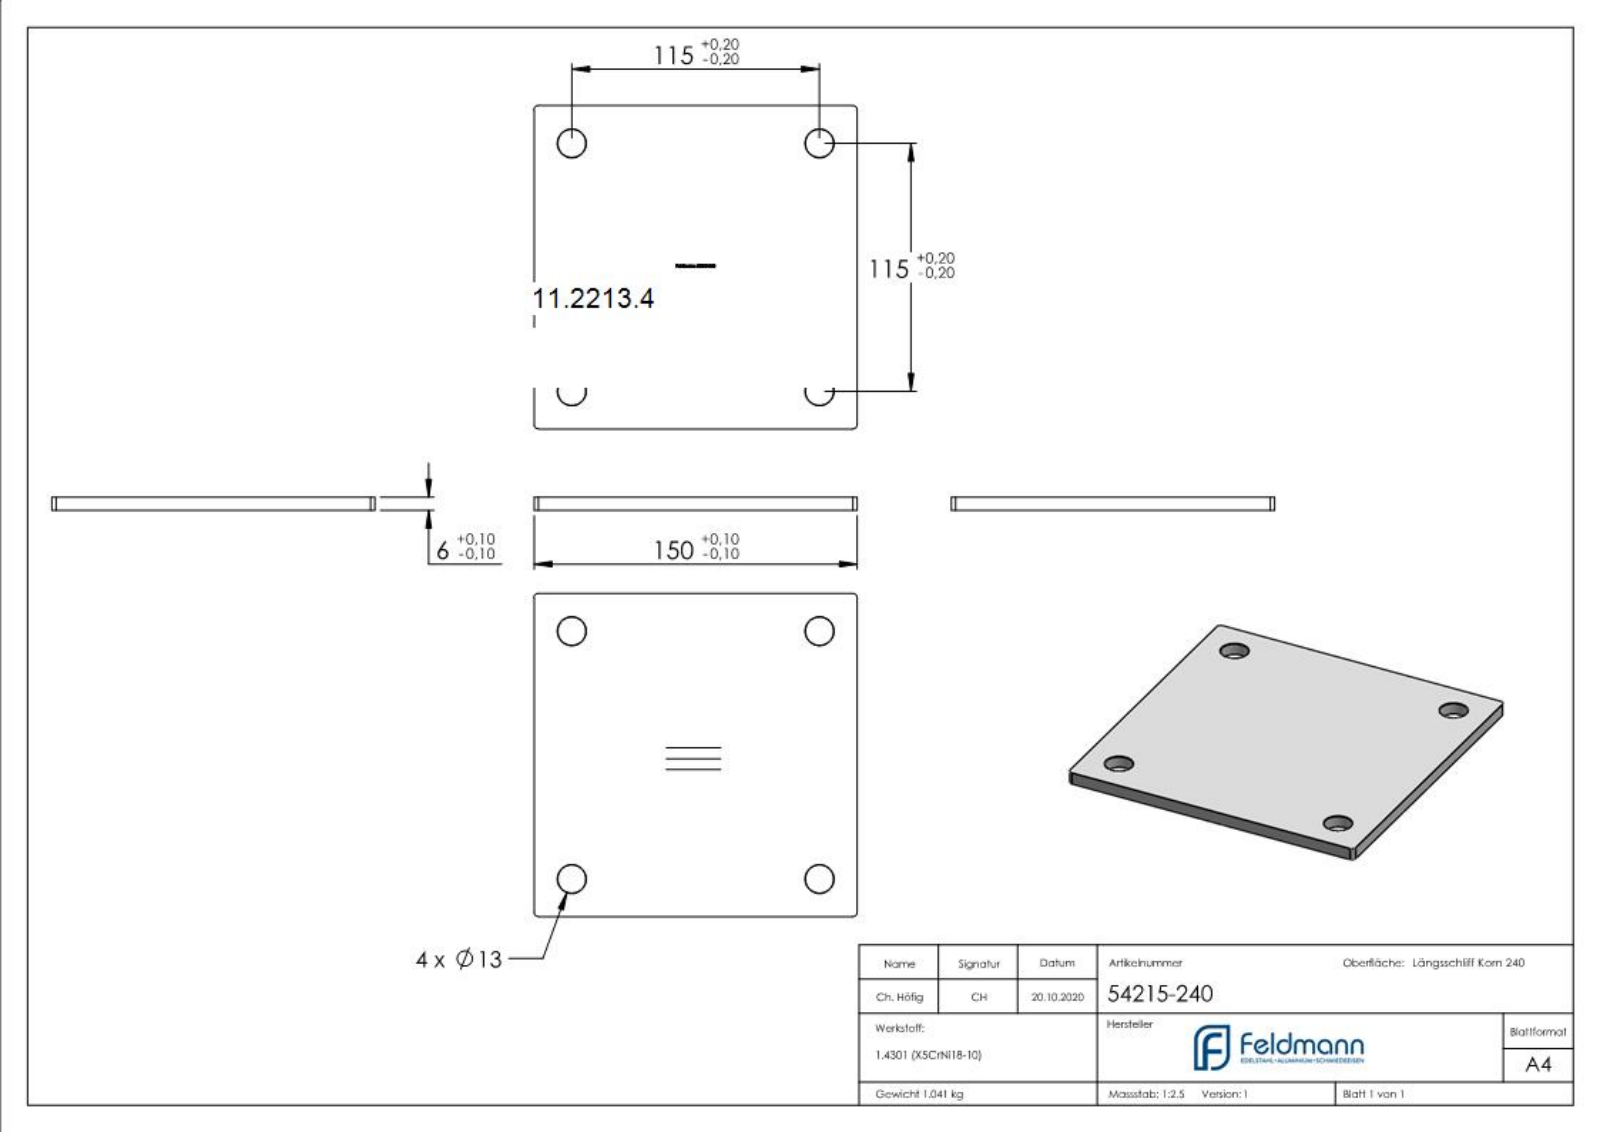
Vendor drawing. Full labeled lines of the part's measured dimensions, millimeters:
Part name (STEP PRODUCT): 54215-240
STEP written by: SolidWorks 2018 (CONFIG_CONTROL_DESIGN)
Units: millimetres
Bodies: 1 solid, 256 faces (143 planar, 12 cylindrical, 101 other)
Overall size (bounding box): 150 × 150 × 6
Volume: 131 783 mm³ · Surface area: 48 453 mm²
Round holes (diameter × count): ⌀13 ×4
Partial cylindrical surfaces — rounded edges, fillets, slot ends (radius × count): R2 ×4
Main face-to-face distances: 6, 150, 5.9, 75, 0.44, 0.88, 1.32, 4.7, 12.75, 1.81
Hole centre spacings: 115, 162.63
